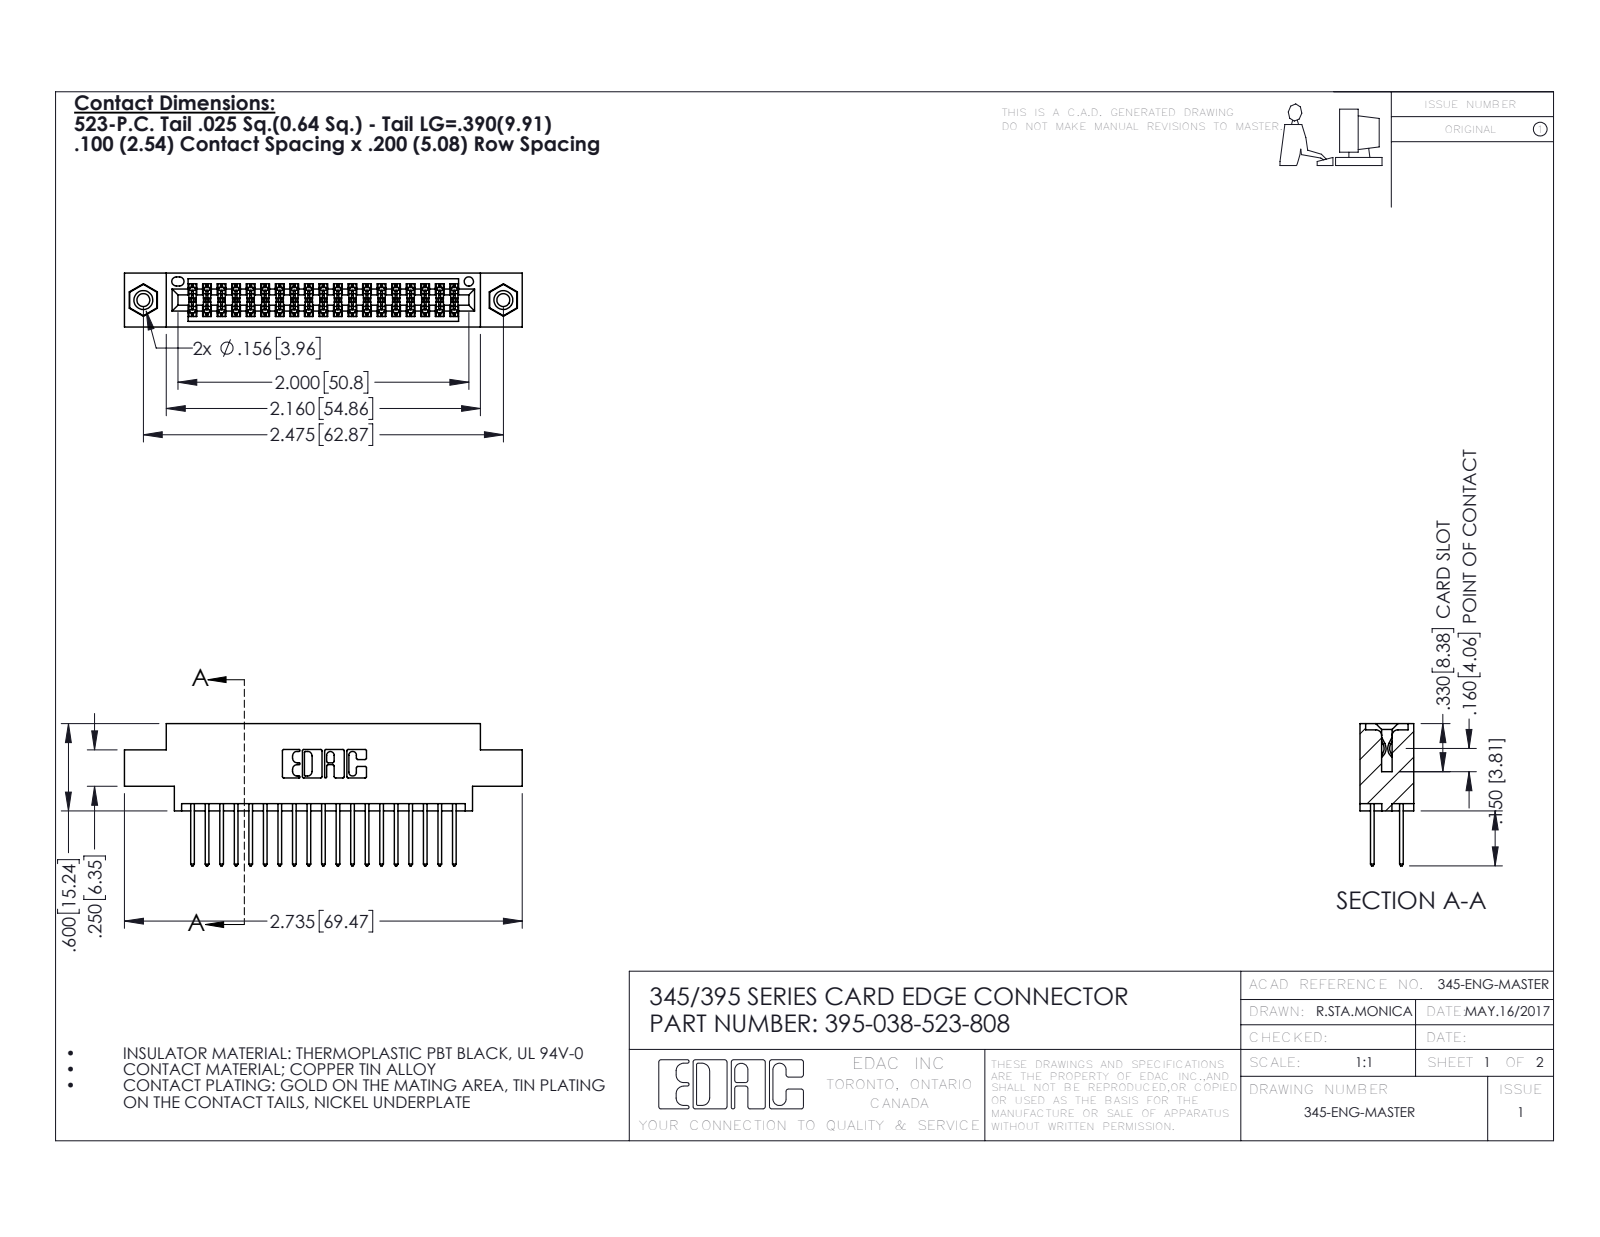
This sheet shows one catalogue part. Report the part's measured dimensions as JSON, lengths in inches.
{"part_name": "345 Part_0.170 Offset - 0.156 Dia-TI; 395-038-523-808; 345-250-001_345-250-003-102; 345-292-001_345-293-123", "step_written_by": "SolidWorks 2016 (CONFIG_CONTROL_DESIGN)", "units": "inches", "bodies": {"solids": 41, "faces": 2090, "planar": 1370, "cylindrical": 704, "other": 16}, "overall_size": [2.735, 0.977, 0.37], "volume_in3": 0.396, "surface_area_in2": 14.97, "round_holes": [[0.089, 2], [0.125, 2], [0.156, 2], [0.064, 1]], "round_bosses_or_shafts": [[0.155, 2]], "partial_cylinders_radius": [[0.006, 57], [0.01, 38], [0.01, 22], [0.007, 6], [0.031, 6], [0.026, 3], [0.014, 2], [0.019, 2]], "face_to_face_distances": [0.072, 0.298, 0.2, 0.37, 0.098, 0.272, 0.025, 0.225, 0.175, 0.1], "hole_center_spacings": [0.27, 2.241, 2.475]}
